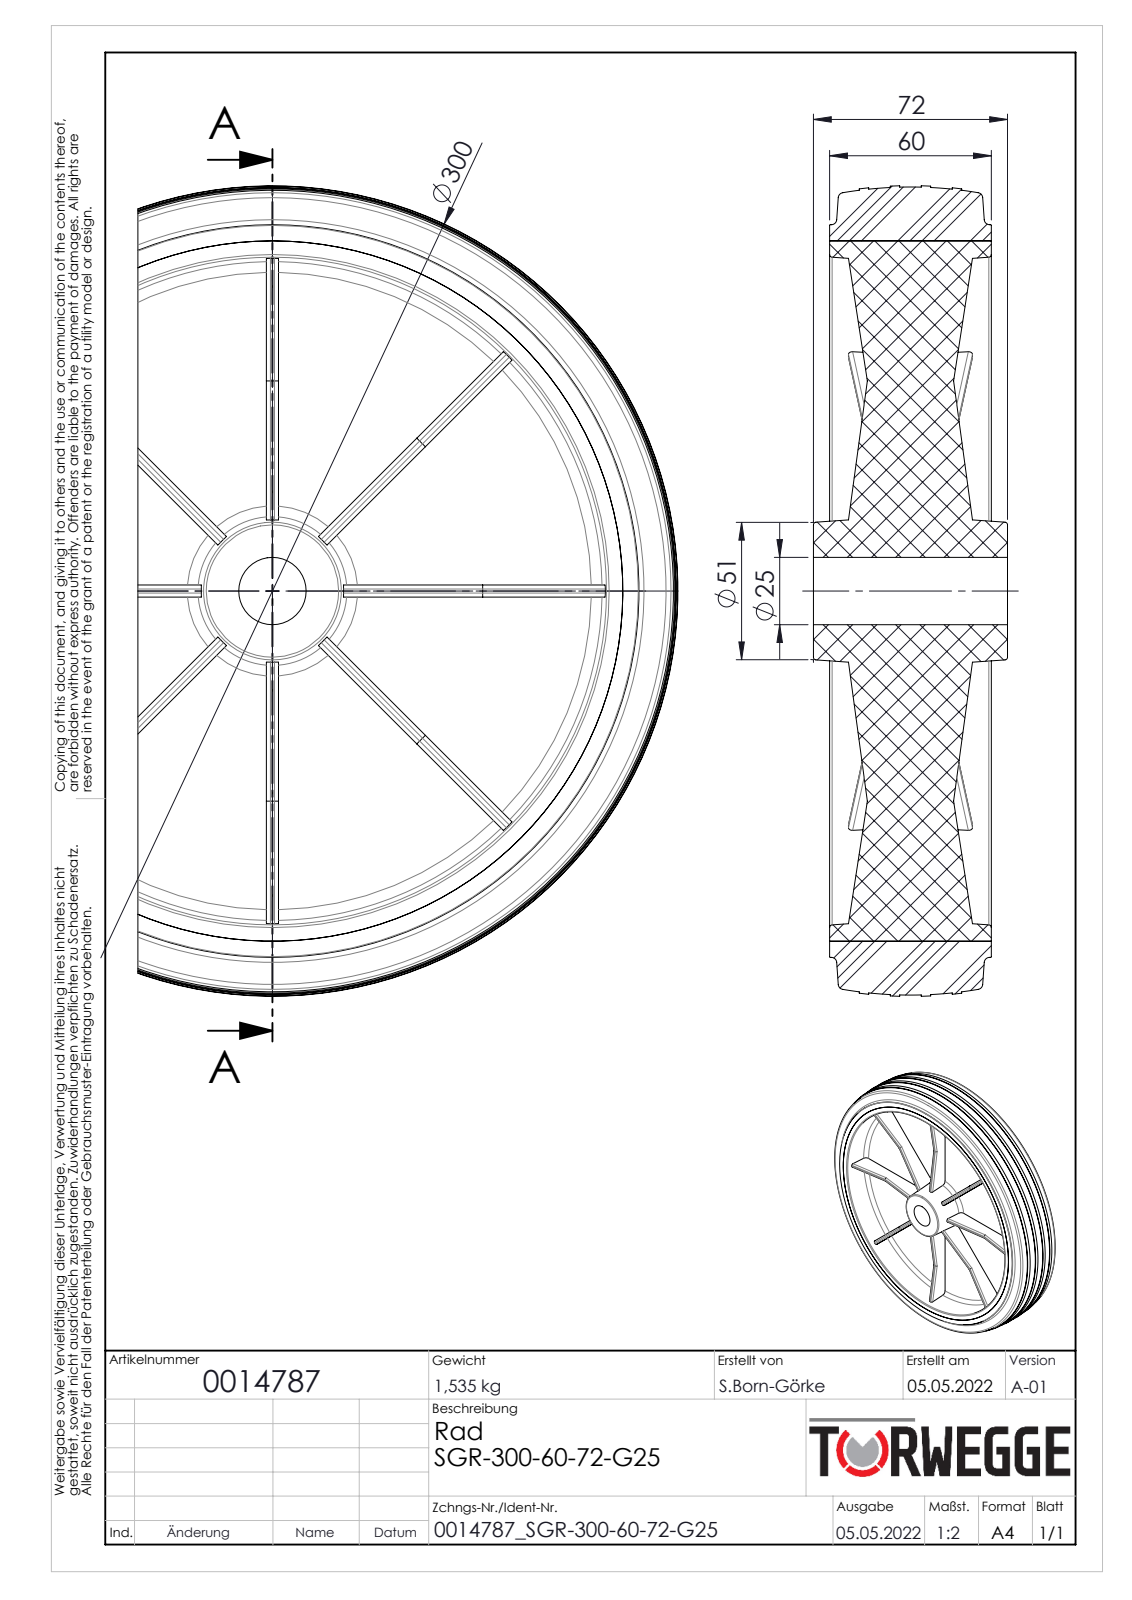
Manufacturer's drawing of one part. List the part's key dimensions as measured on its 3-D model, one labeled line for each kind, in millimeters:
Part name (STEP PRODUCT): 0014787
STEP written by: SolidWorks 2020 (AUTOMOTIVE_DESIGN)
Units: millimetres
Bodies: 2 solids, 250 faces (94 planar, 74 cylindrical, 82 other)
Overall size (bounding box): 300.89 × 300.89 × 72
Volume: 1 711 000 mm³ · Surface area: 392 025 mm²
Round holes (diameter × count): ⌀25 ×1, ⌀260 ×1
Round bosses / shafts (diameter × count): ⌀272 ×1
Partial cylindrical surfaces — rounded edges, fillets, slot ends (radius × count): R1.5 ×64
Main face-to-face distances: 4, 4.5, 32, 28, 60, 6, 34, 38, 11.5, 66
